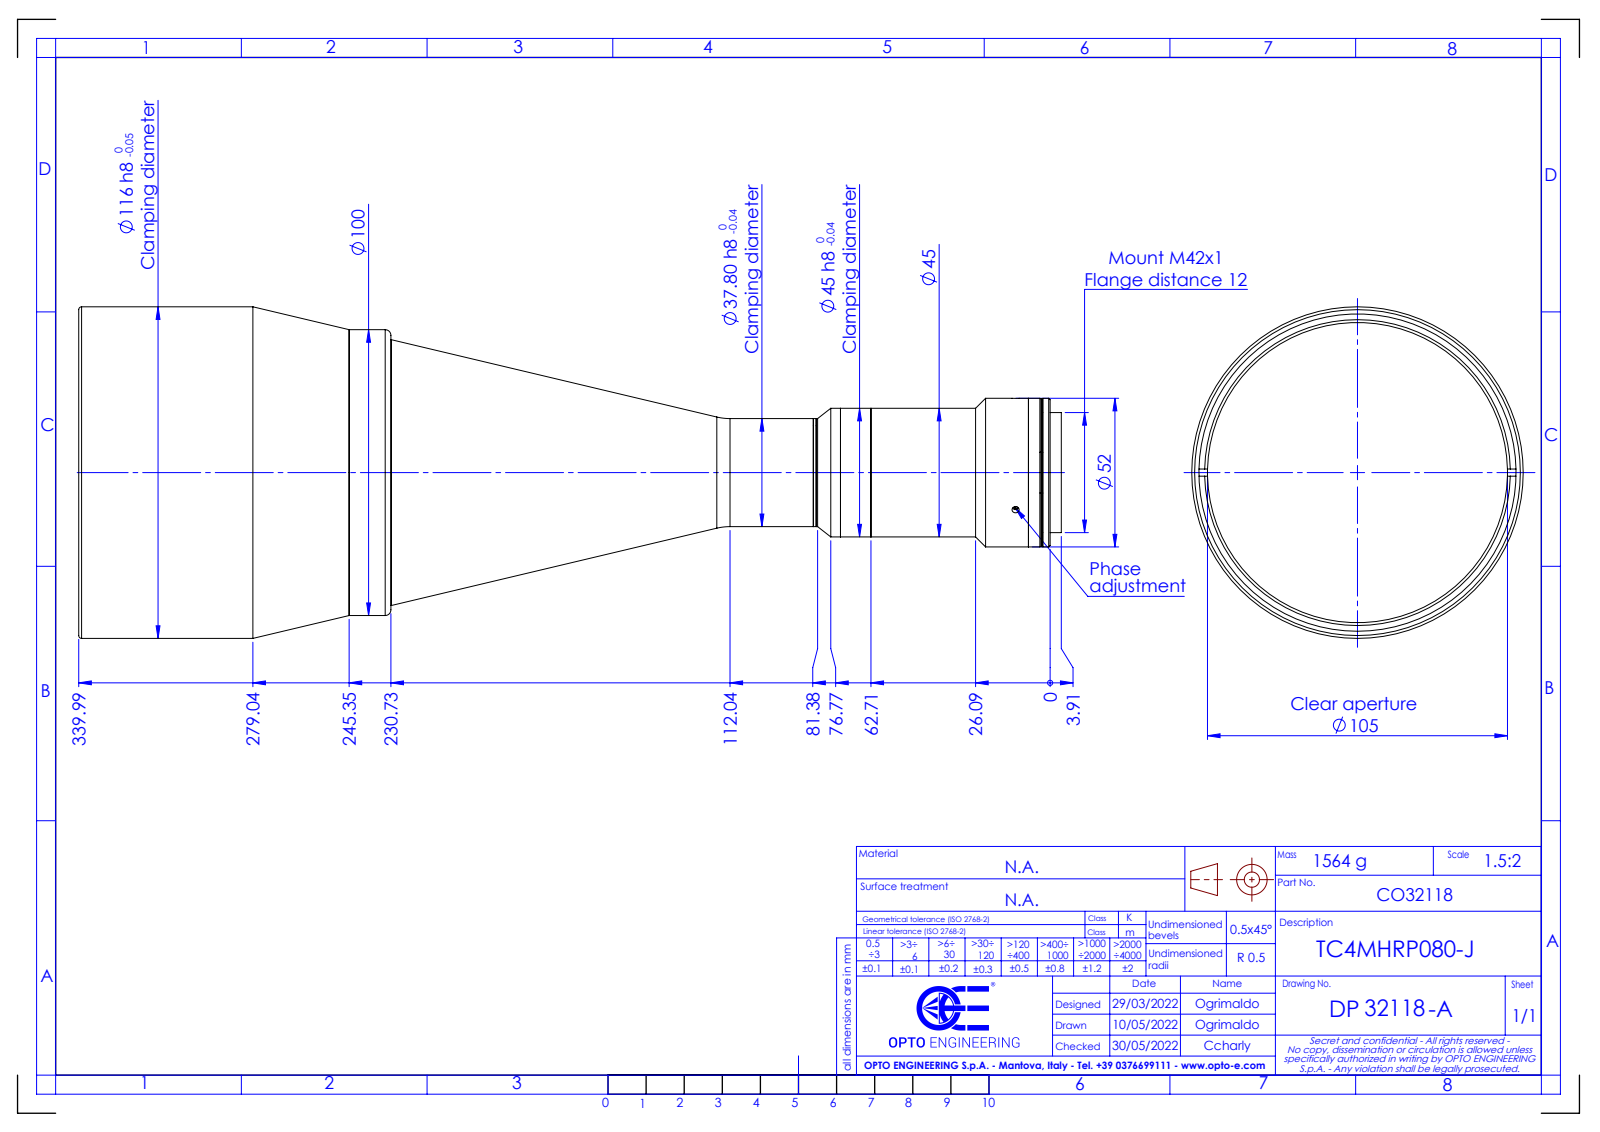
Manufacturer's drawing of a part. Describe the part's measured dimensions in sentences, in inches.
The part is named "DP32118-A_TC4MHRP080-J". Its 3-D file was written by "SolidWorks 2021 (CONFIG_CONTROL_DESIGN)". It is 0 solids with 86 faces: 20 planar, 42 cylindrical and 24 other. Overall it measures 13.539 by 4.567 by 4.567 inches. Round holes: 3 of diameter 0.098, 1 of diameter 1.496, 1 of diameter 4.134, 1 of diameter 4.37. Round bosses or shafts: 1 of diameter 4.567, 1 of diameter 3.937, 1 of diameter 3.661, 1 of diameter 2.047, 1 of diameter 2.039, 1 of diameter 1.772, 1 of diameter 1.654, 1 of diameter 1.488. The main face-to-face distances are 3.705, 13.263, 9.559, 13.223, 9.518, 0.041, 13.364, 9.659, 0.141, 0.1.
